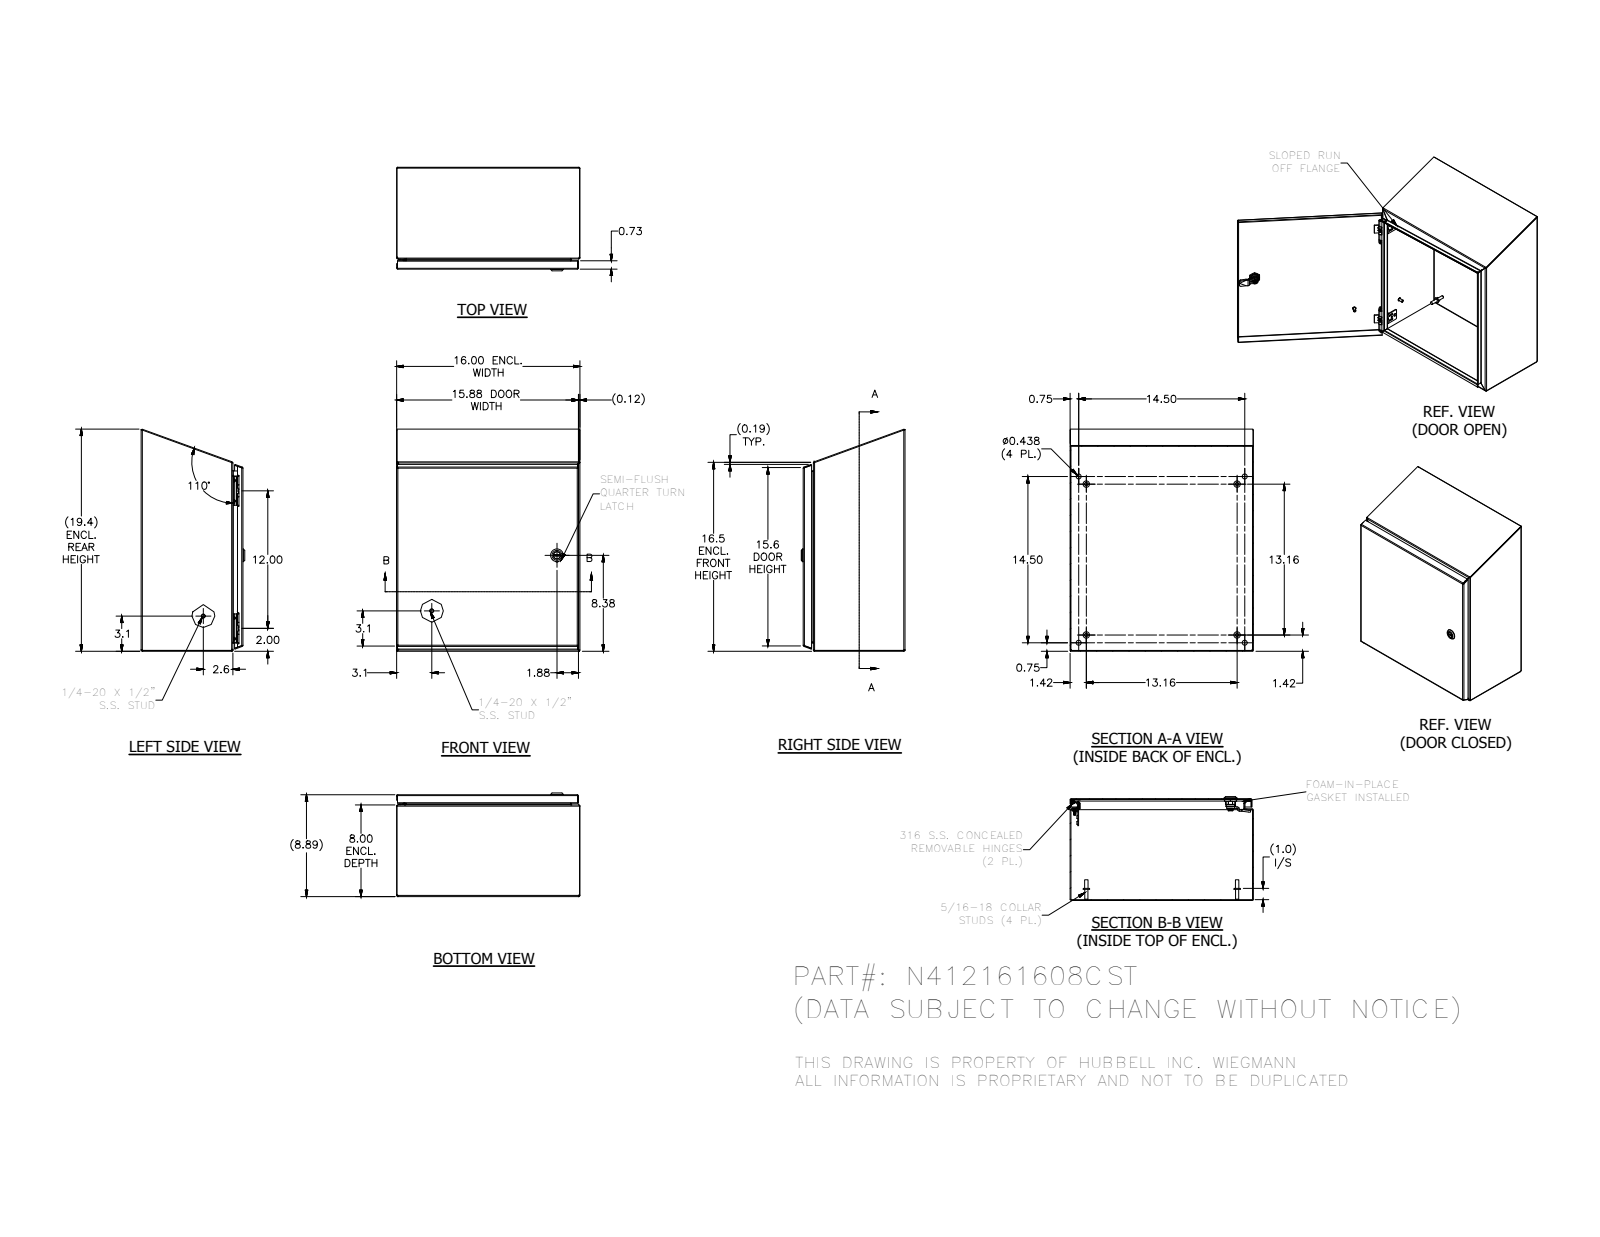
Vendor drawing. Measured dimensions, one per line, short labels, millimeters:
name: N412161608CST
written by: SolidWorks 2018 (AUTOMOTIVE_DESIGN)
unit: mm
bodies: 36 solids, 1521 faces (568 planar, 552 cylindrical, 401 other)
size: 492.5 × 406.4 × 229.7
volume: 1 529 000 mm³; area: 1 638 000 mm²
holes: 4× ⌀2.4, 4× ⌀3.9, 4× ⌀4.2, 4× ⌀4.4, 4× ⌀4.7, 4× ⌀11.1, 3× ⌀4, 1× ⌀4.7, 1× ⌀5, 1× ⌀8, 1× ⌀10, 1× ⌀10.2
bosses: 10× ⌀6.4, 4× ⌀14.3, 4× ⌀9.1, 4× ⌀8.1, 4× ⌀7.6, 4× ⌀7, 4× ⌀6.5, 4× ⌀4.2
rounds: 30× R0.3, 29× R0.8, 26× R1.3, 19× R2.7, 18× R0.4, 16× R3.2, 13× R0.5, 8× R0.8
face distances: 1.9, 223.9, 404.5, 222, 225.7, 402.6, 406.4, 201.3, 22.5, 20.7
hole spacings: 304.8, 368.3, 12.7, 16.7, 16.8, 25, 33.2, 33.3
